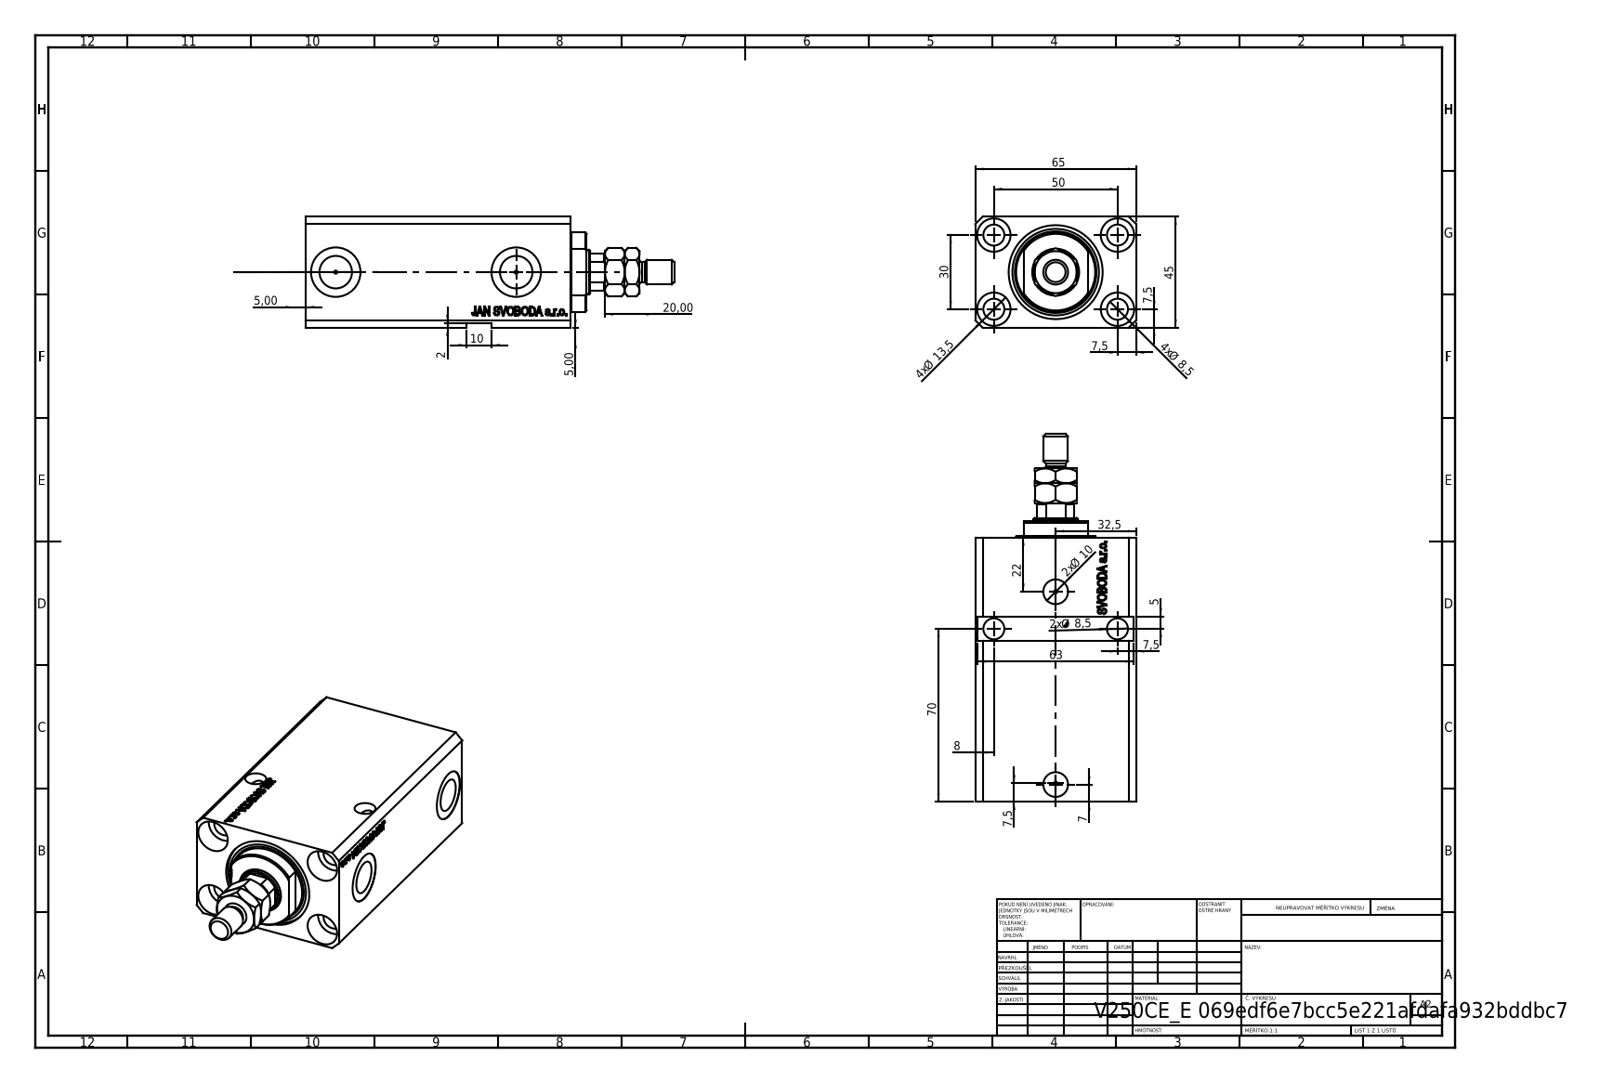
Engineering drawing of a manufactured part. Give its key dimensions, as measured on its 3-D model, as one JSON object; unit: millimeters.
{"part_name": "V250CE_E_Body; V250CE_C_VCP; V250CE_VC_E; MTA", "step_written_by": "SolidWorks 2019 (CONFIG_CONTROL_DESIGN)", "units": "millimeters", "bodies": {"solids": 4, "faces": 962, "planar": 454, "cylindrical": 100, "other": 408}, "overall_size": [148.9, 65, 45], "volume_mm3": 265891, "surface_area_mm2": 70860, "round_holes": [[8.5, 7], [1.25, 4], [13.5, 4], [10, 2], [13.16, 2], [20, 2], [18, 1], [25, 1], [38, 1]], "round_bosses_or_shafts": [[10, 1], [8, 1]], "partial_cylinders_radius": [[8.5, 1], [16, 1]], "face_to_face_distances": [45, 65, 81.9, 107, 25.1, 6.9, 75, 100.1, 64.9, 9], "hole_center_spacings": [29.15, 50, 30, 58.31, 67.29, 67.78, 0.53, 73]}
